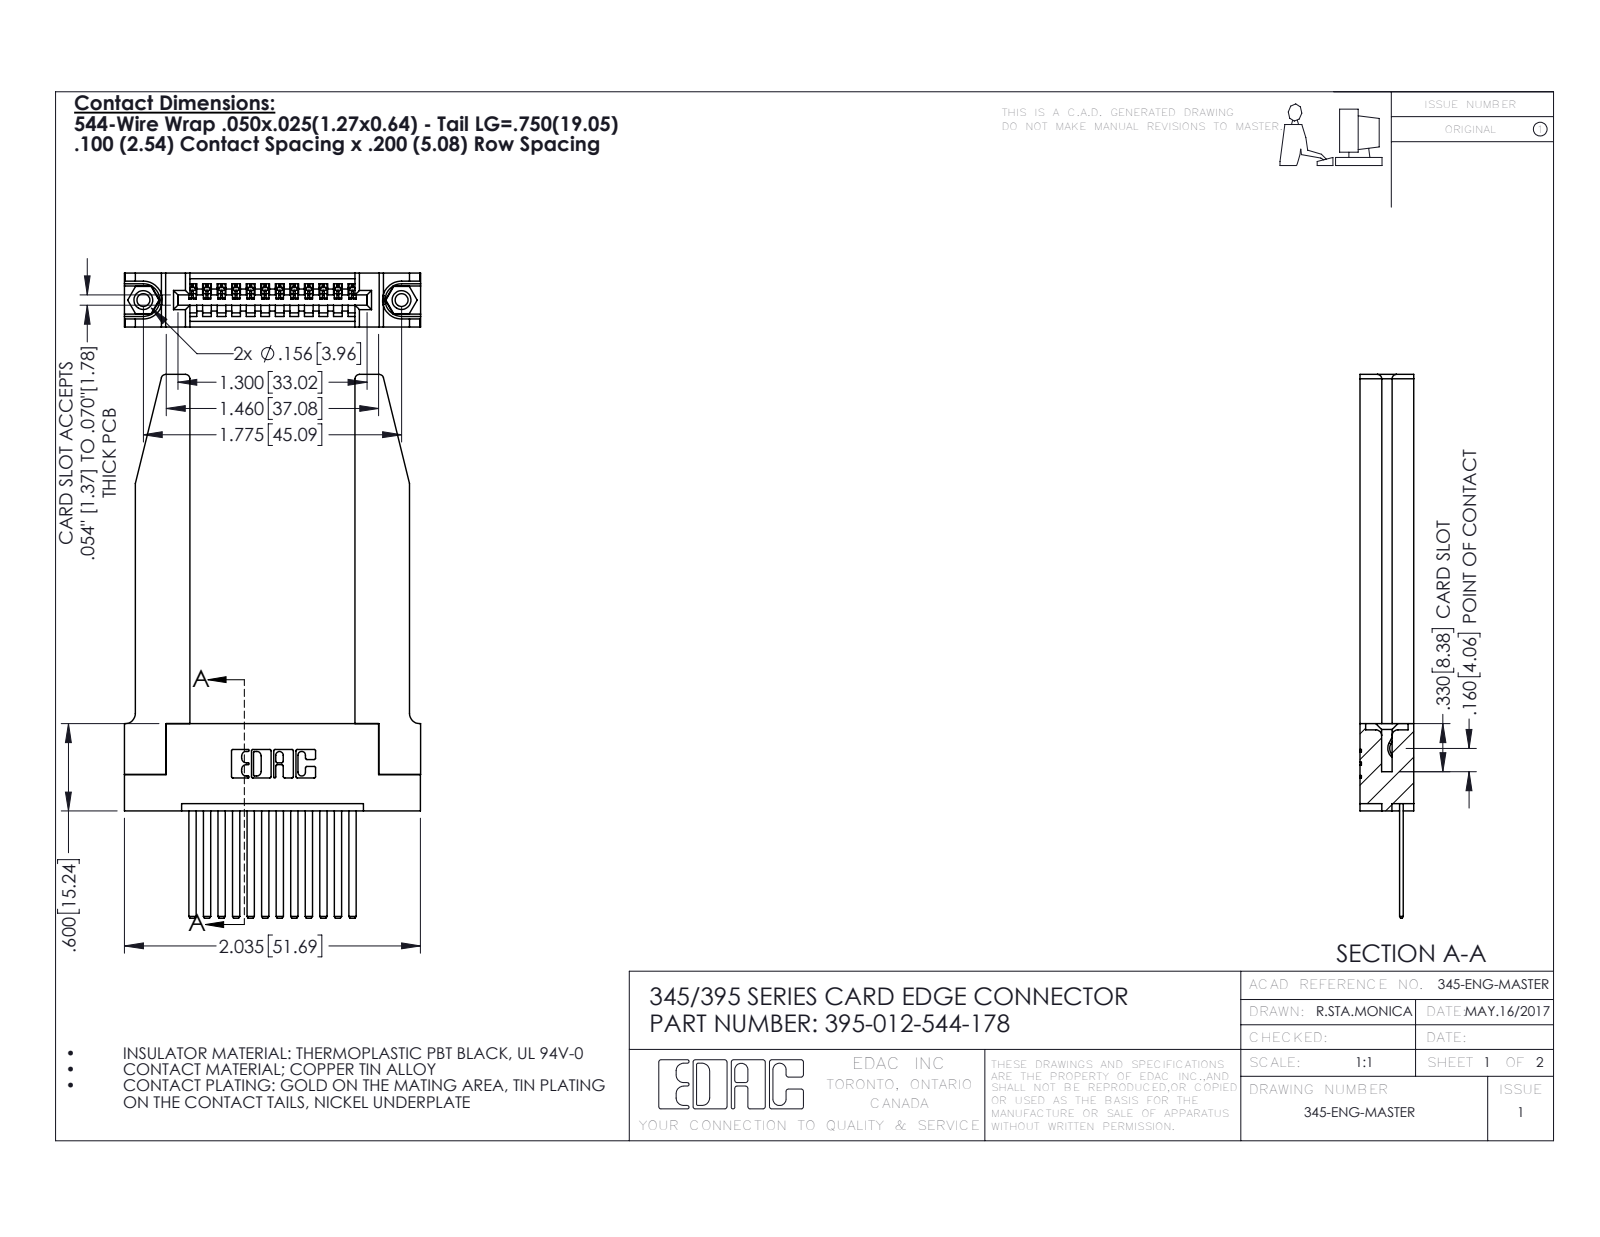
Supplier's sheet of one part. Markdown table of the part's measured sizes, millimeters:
| quantity | value |
| --- | --- |
| part name | 345-220-078_345-220-078; 345 Part_Flush Mounting Lugs - 0.156 Dia-TH; 345-250-001_345-250-001-102; 345-292-001_345-293-144 (+1 more) |
| STEP written by | SolidWorks 2016 (CONFIG_CONTROL_DESIGN) |
| units | millimeters |
| bodies | 17 solids, 984 faces (654 planar, 278 cylindrical, 52 other) |
| overall size | 94.9 × 51.7 × 9.4 |
| volume | 12 600 mm³ |
| surface area | 13 240 mm² |
| round holes (diameter × count) | 2.3 × 2, 3.2 × 2, 4 × 2, 1.6 × 1 |
| round bosses / shafts (diameter × count) | 3.9 × 2 |
| partial cylindrical surfaces (radius × count) | 0.2 × 24, 0.3 × 22, 0.8 × 8, 0.2 × 6, 0.8 × 6, 0.7 × 3, 0.8 × 2, 1 × 2 |
| main face-to-face distances | 9.4, 1.8, 7.6, 5.1, 2.5, 6.9, 0.6, 3.8, 3.8, 2 |
| hole center spacings | 6.9, 39.2, 45.1 |
